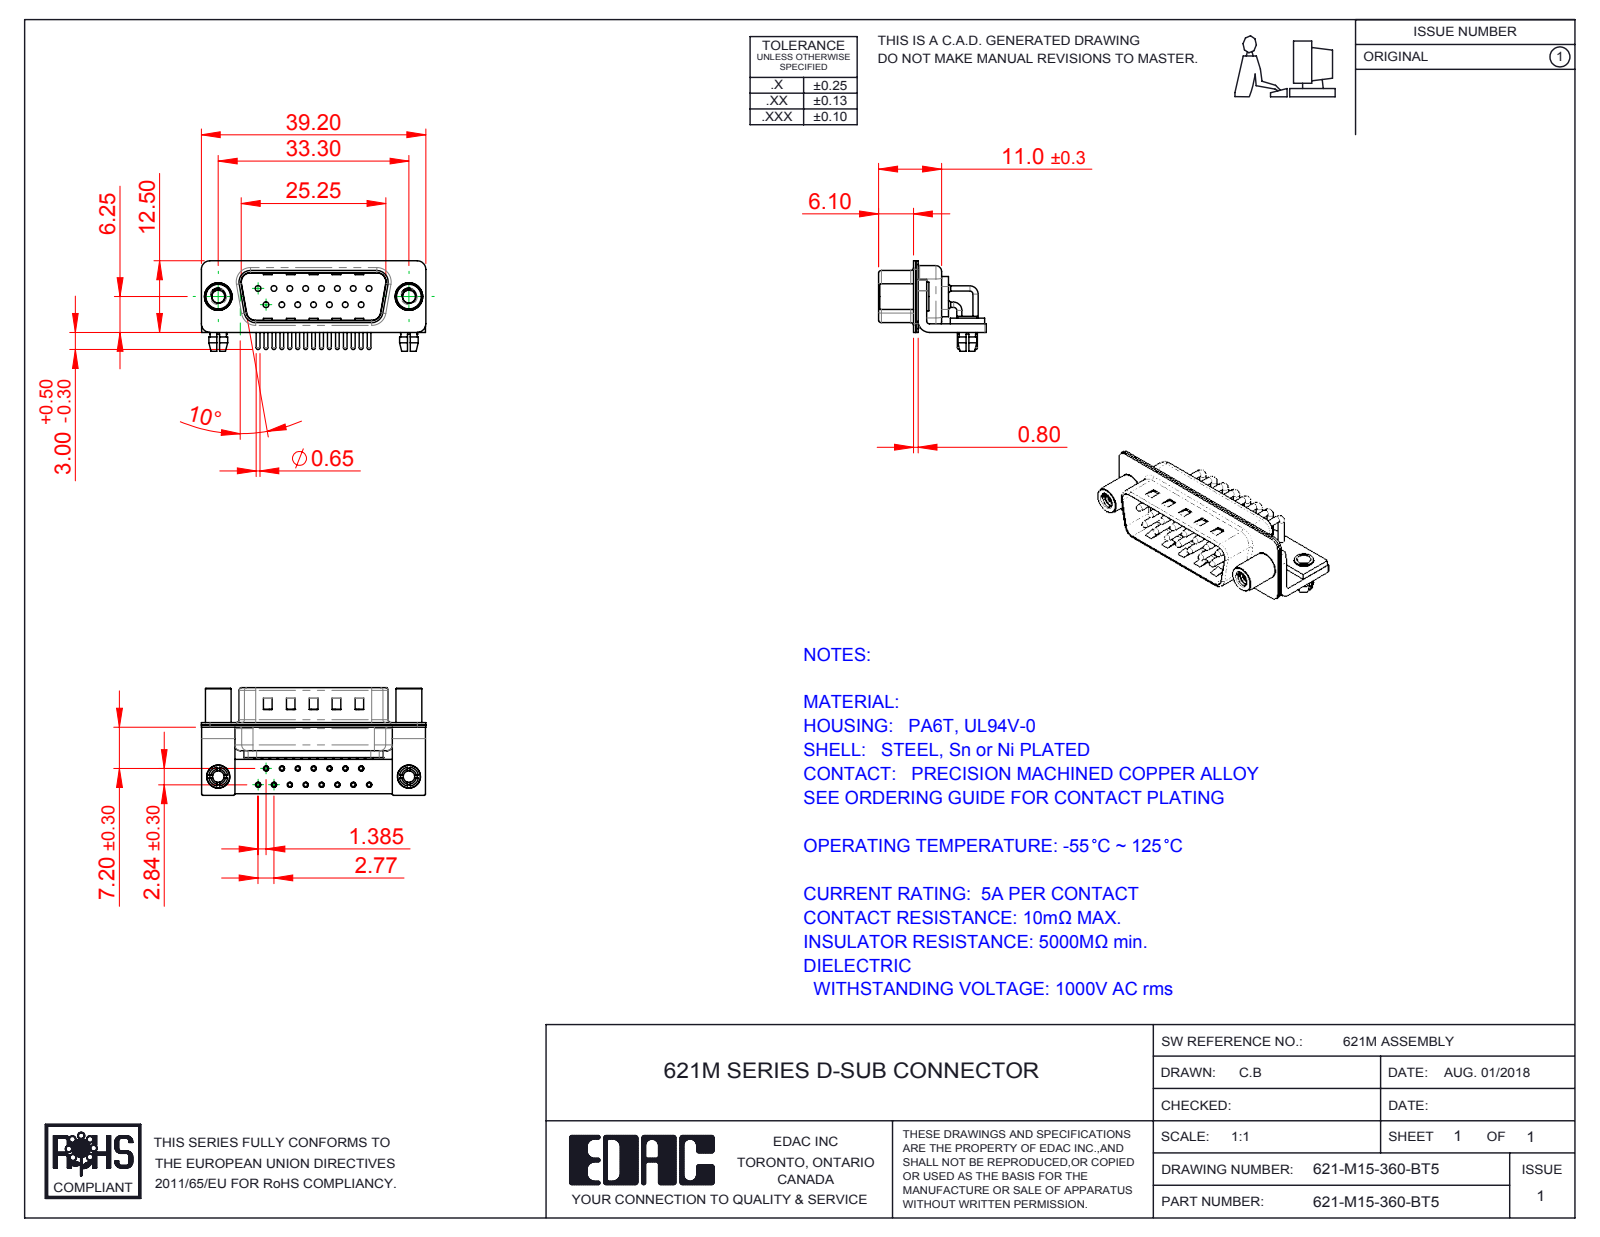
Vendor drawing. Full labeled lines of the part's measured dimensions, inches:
Part name (STEP PRODUCT): 621M Stabilizer Board_15 Contacts; 621M Stabilizer Bracket; 621M Contact Row 2; 621M Housing_15 Contacts (+6 more)
STEP written by: SolidWorks 2016 (CONFIG_CONTROL_DESIGN)
Units: inches
Bodies: 25 solids, 2212 faces (1175 planar, 799 cylindrical, 238 other)
Overall size (bounding box): 1.543 × 0.74 × 0.622
Volume: 0.155 in³ · Surface area: 10.72 in²
Round holes (diameter × count): ⌀0.079 ×17, ⌀0.035 ×15, ⌀0.039 ×15, ⌀0.067 ×15, ⌀0.089 ×2, ⌀0.098 ×2, ⌀0.126 ×2, ⌀0.157 ×2, ⌀0.189 ×2
Round bosses / shafts (diameter × count): ⌀0.035 ×22, ⌀0.059 ×15, ⌀0.026 ×15, ⌀0.197 ×2, ⌀0.193 ×2, ⌀0.177 ×2, ⌀0.157 ×2, ⌀0.134 ×2
Partial cylindrical surfaces — rounded edges, fillets, slot ends (radius × count): R0.01 ×16, R0.059 ×16, R0.04 ×15, R0.079 ×13, R0.02 ×9, R0.063 ×8, R0.024 ×4, R0.026 ×4
Main face-to-face distances: 0.016, 0.033, 0.059, 0.031, 0.049, 0.409, 0.376, 0.039, 0.075, 0.327
Hole centre spacings: 0.124, 0.109, 0.218, 0.327, 0.436, 0.198, 0.198, 0.294
